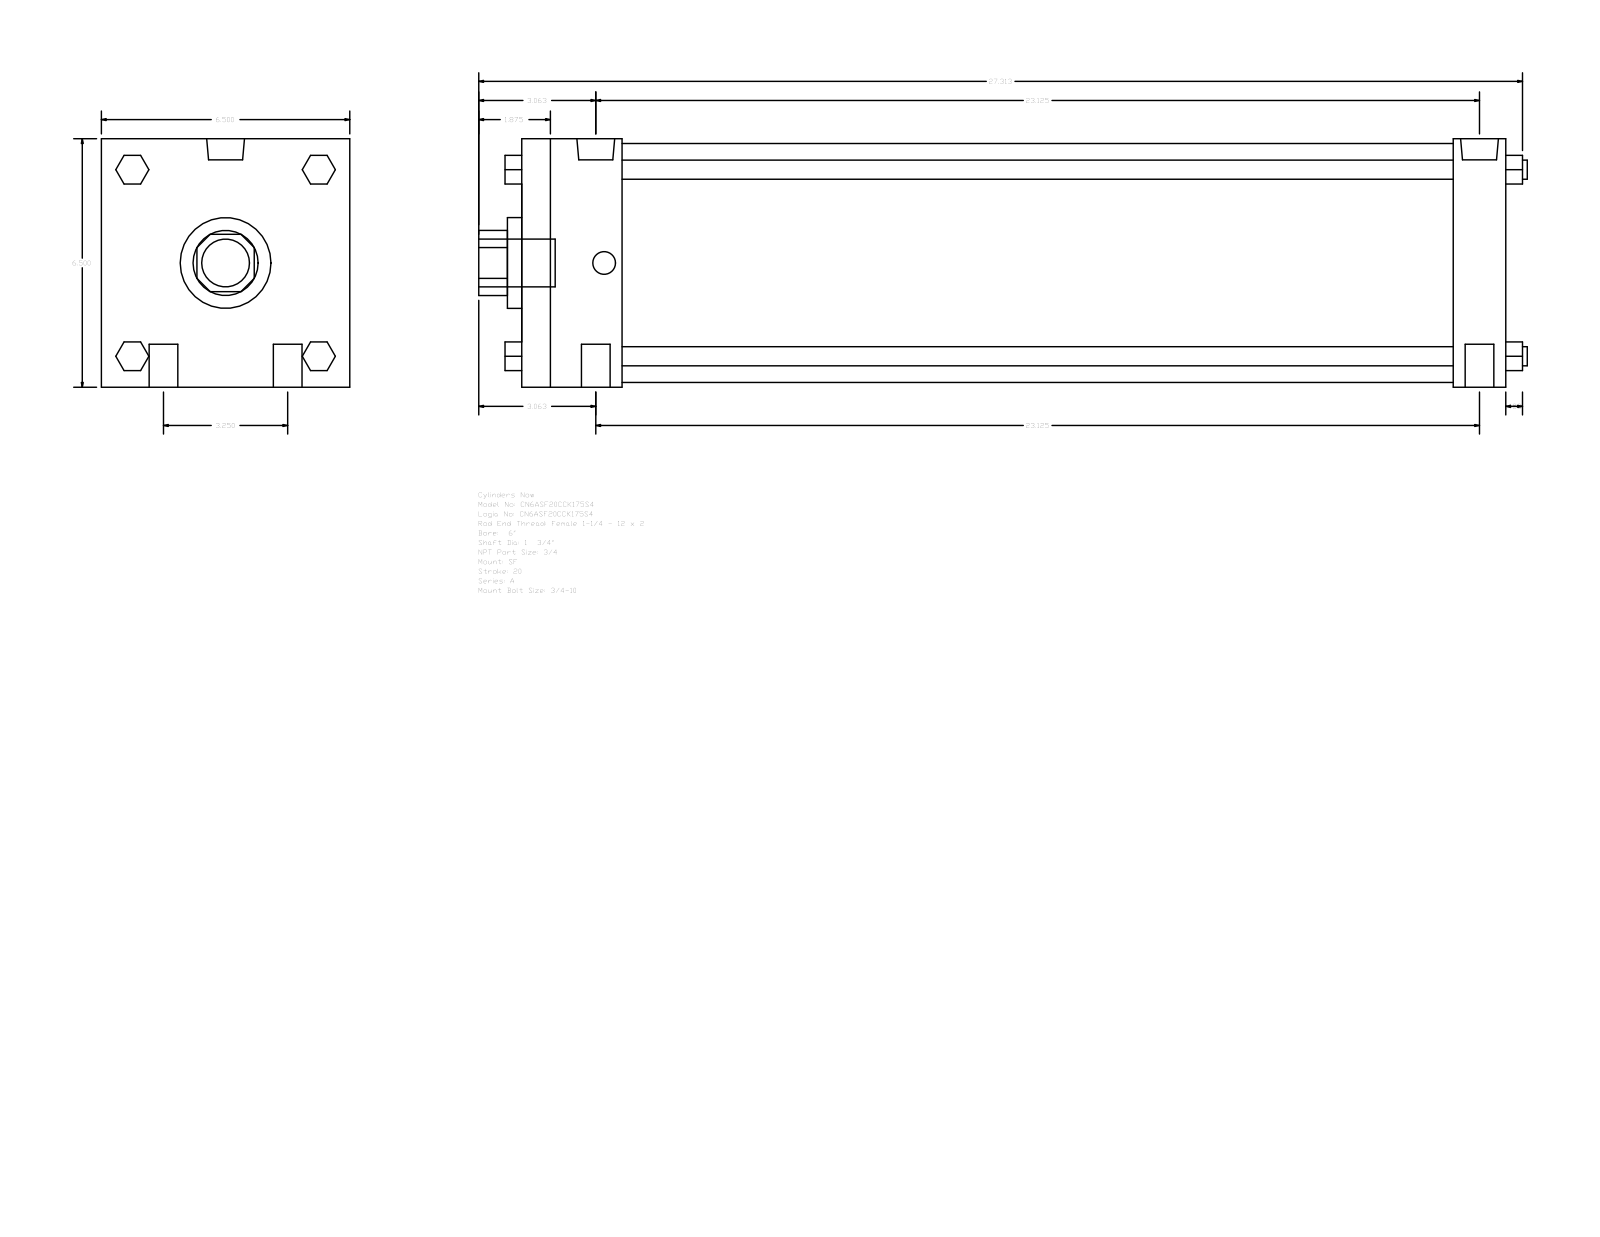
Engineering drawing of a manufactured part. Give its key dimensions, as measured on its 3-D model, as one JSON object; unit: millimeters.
{"part_name": "A_SF__0600_1.75", "step_written_by": "GSSL Pune (CONFIG_CONTROL_DESIGN)", "units": "millimeters", "bodies": {"solids": 0, "faces": 124, "planar": 94, "cylindrical": 30, "other": 0}, "overall_size": [696.91, 165.1, 165.1], "round_holes": [[44.45, 1], [60.33, 1], [158.75, 1]], "round_bosses_or_shafts": [[19.05, 4], [12.7, 4], [25.12, 2], [15.08, 2], [31.75, 1]], "partial_cylinders_radius": [[21.63, 1]], "face_to_face_distances": [165.1, 654.05, 34.92, 619.13, 66.68, 552.45, 587.37, 19.05, 61.97, 107.34]}
